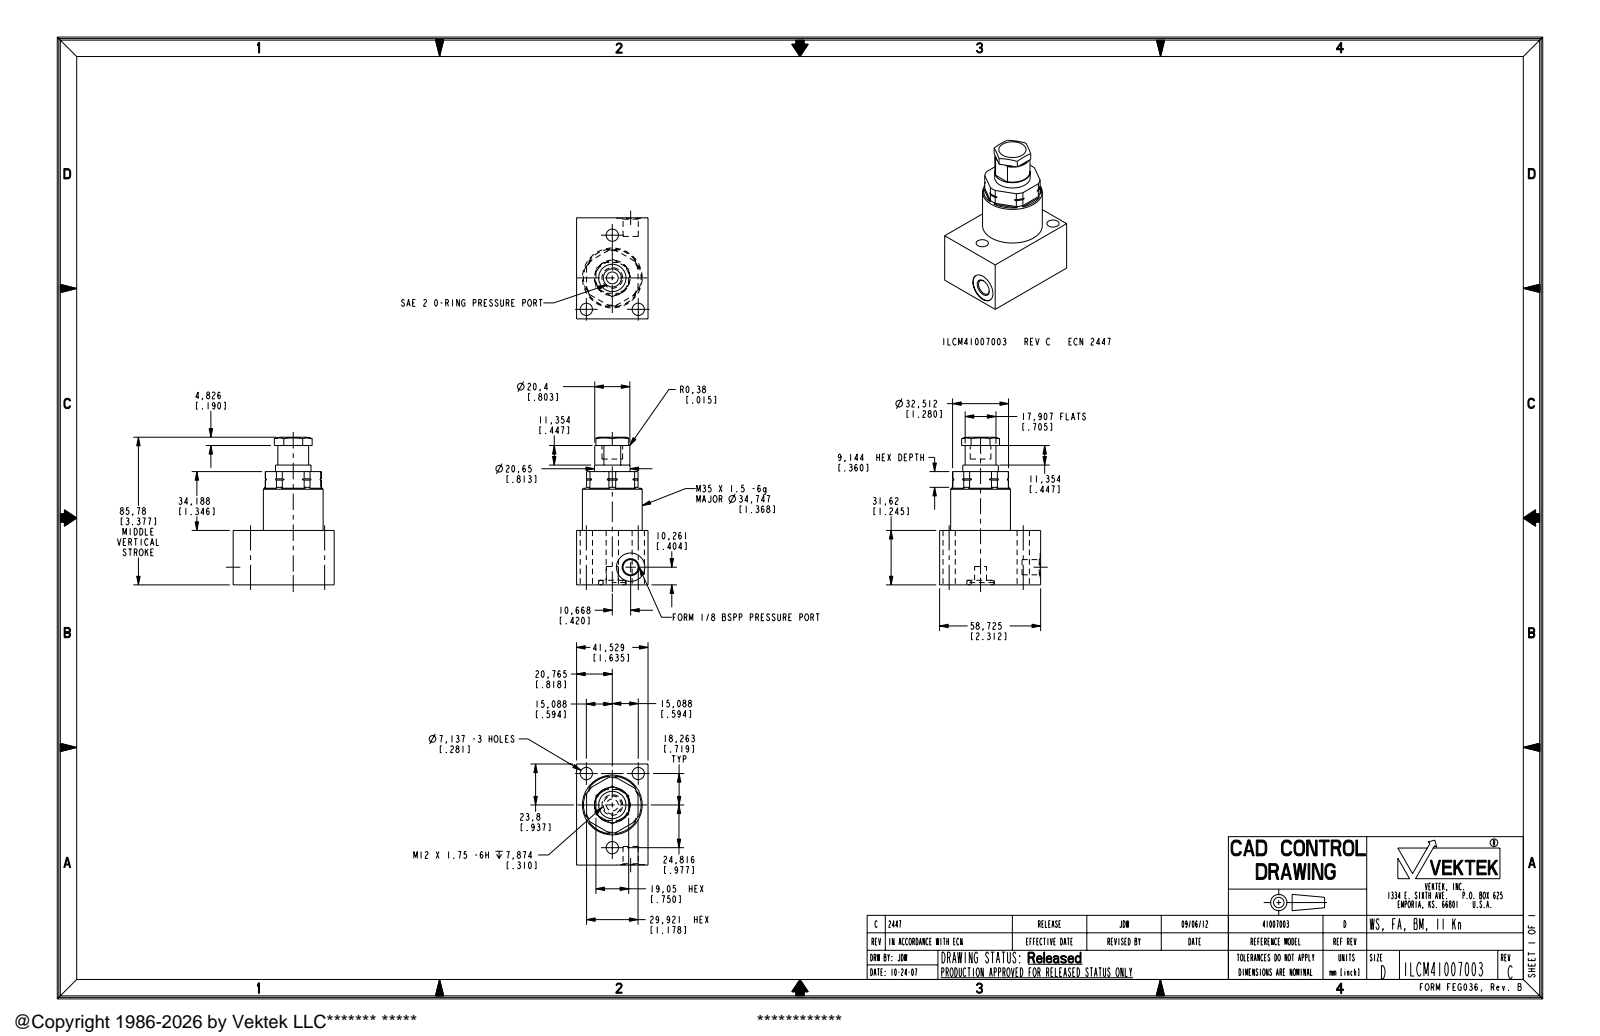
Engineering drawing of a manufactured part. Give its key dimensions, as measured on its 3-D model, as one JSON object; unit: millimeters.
{"part_name": "ILCM41007003", "step_written_by": "PRO/ENGINEER BY PARAMETRIC TECHNOLOGY CORPORATION, 2007460 (AUTOMOTIVE_DESIGN_CC2)", "units": "millimeters", "bodies": {"solids": 1, "faces": 109, "planar": 48, "cylindrical": 41, "other": 20}, "overall_size": [85.78, 58.73, 41.53], "volume_mm3": 108023, "surface_area_mm2": 19461, "round_holes": [[7.14, 3], [6.91, 1], [8.84, 1], [11.99, 1], [15.88, 1], [16.51, 1]], "round_bosses_or_shafts": [[34.75, 1], [20.65, 1]], "partial_cylinders_radius": [[0.51, 6], [10.2, 1], [16.26, 1]], "face_to_face_distances": [41.52, 31.62, 58.72, 65.81, 34.19, 29.92, 5.8, 35.72, 85.78, 54.16], "hole_center_spacings": [23.69, 45.65, 24.82, 30.18]}
